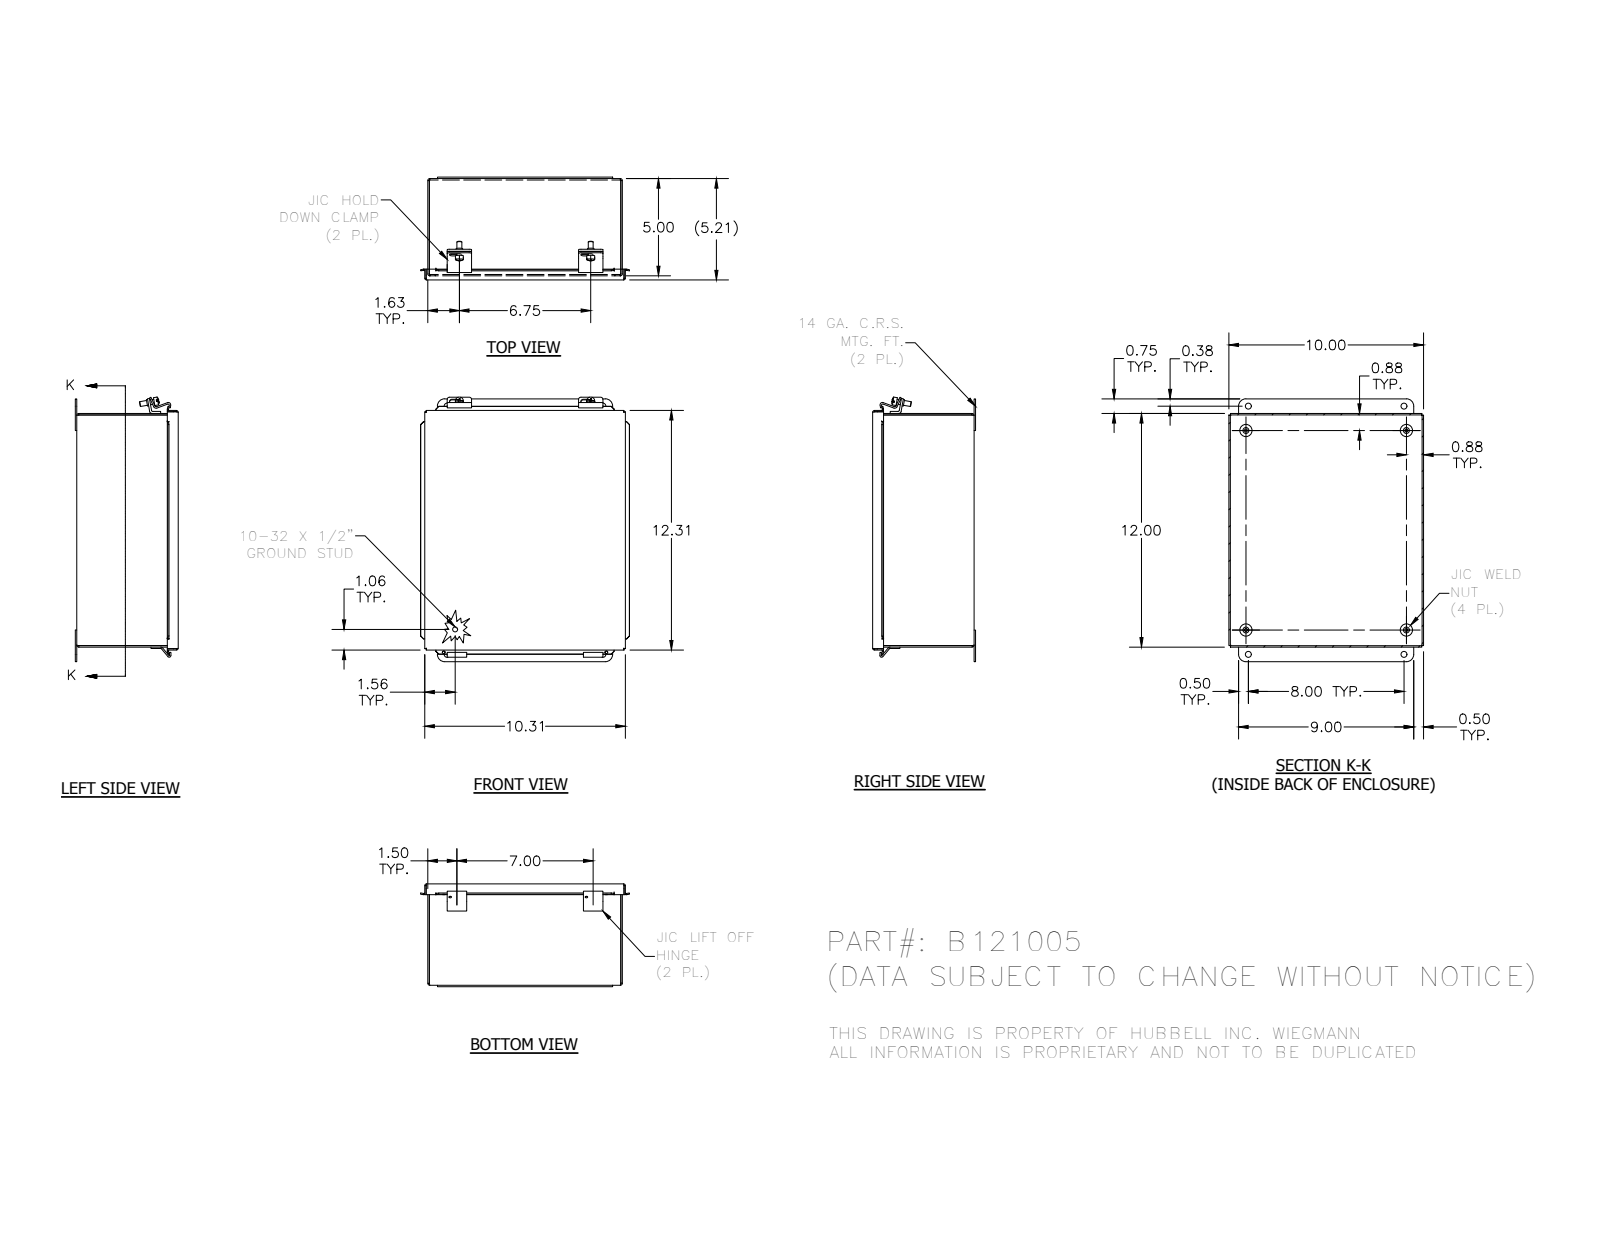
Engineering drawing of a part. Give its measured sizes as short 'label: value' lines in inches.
name: B121005; 3499; 3484; C1001 (+7 more)
written by: Autodesk Inventor 2012 (AUTOMOTIVE_DESIGN)
unit: in
bodies: 19 solids, 422 faces (279 planar, 98 cylindrical, 45 other)
size: 13.593 × 10.739 × 5.287
volume: 43.33 in³; area: 1 168 in²
holes: 4× ⌀0.156, 4× ⌀0.31, 2× ⌀0.125, 2× ⌀0.14, 2× ⌀0.196
bosses: 4× ⌀0.625, 4× ⌀0.3, 3× ⌀0.25, 2× ⌀0.41, 2× ⌀0.344, 1× ⌀0.19
rounds: 16× R0.031, 8× R0.093, 8× R0.105, 8× R0.125, 4× R0.133, 4× R0.375, 3× R0.063, 3× R0.126
face distances: 0.074, 5.15, 0.062, 5.212, 5.076, 5.138, 9.926, 11.926, 9.852, 10
hole spacings: 14.081, 1.256, 1.257, 8, 8.22, 8.221, 8.25, 10.25
